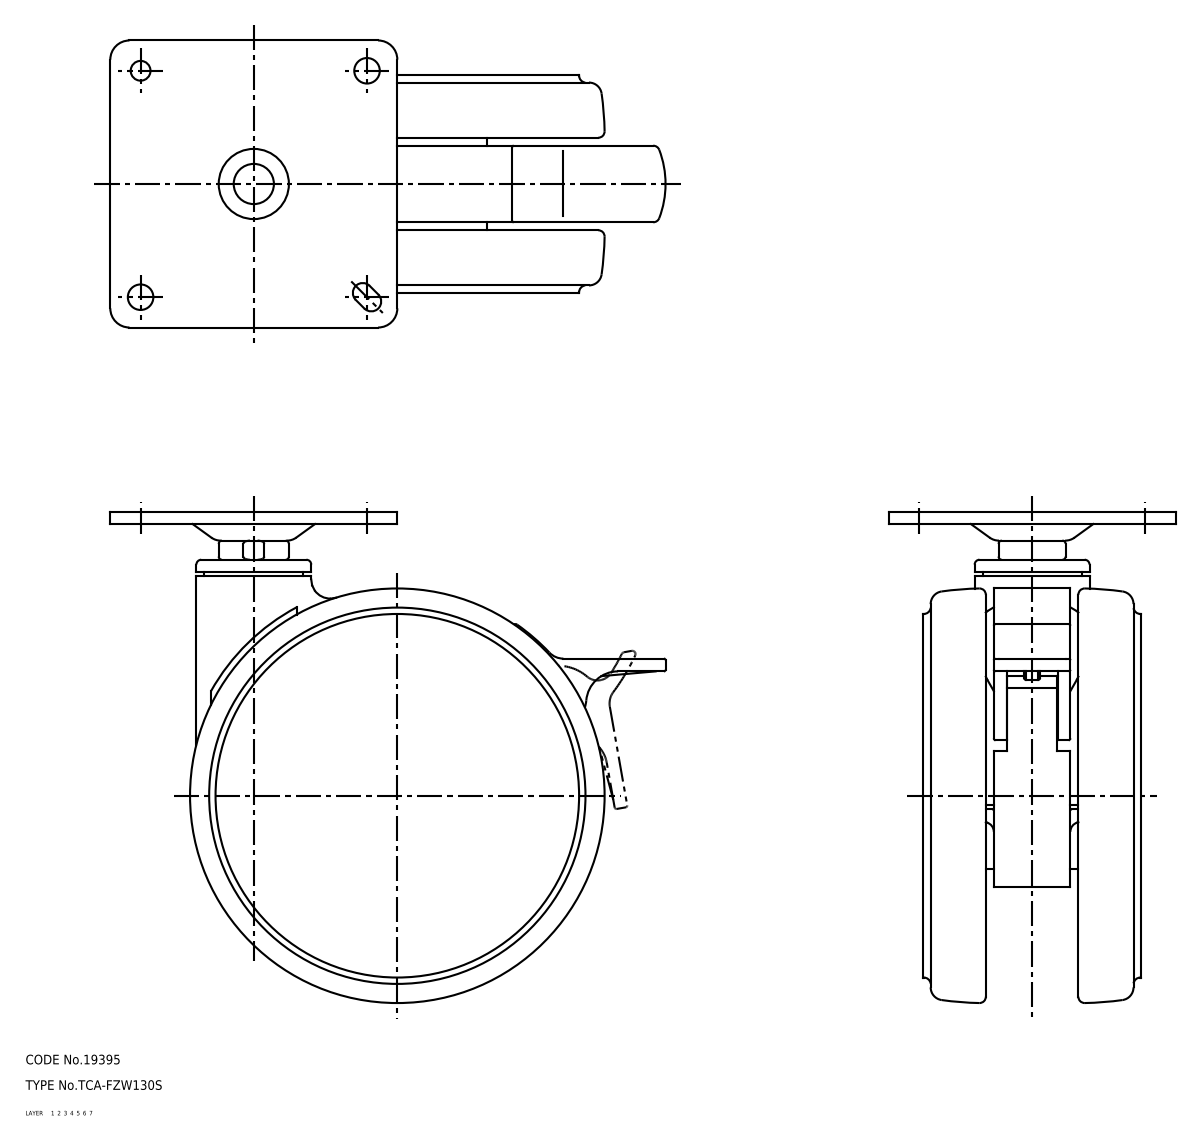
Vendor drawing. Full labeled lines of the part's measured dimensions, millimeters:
Part name (STEP PRODUCT): caster; TCA-FZW130S
STEP written by: SolidWorks 2015 (AUTOMOTIVE_DESIGN)
Units: millimetres
Bodies: 1 solid, 2612 faces (776 planar, 1126 cylindrical, 710 other)
Overall size (bounding box): 174.11 × 154 × 90
Volume: 541 887 mm³ · Surface area: 209 290 mm²
Round holes (diameter × count): ⌀3 ×2, ⌀3.25 ×2, ⌀8 ×2, ⌀1.8 ×1, ⌀3.2 ×1, ⌀6.2 ×1, ⌀9.1 ×1, ⌀10 ×1, ⌀10.1 ×1, ⌀10.5 ×1, ⌀11.5 ×1, ⌀12 ×1
Round bosses / shafts (diameter × count): ⌀117.8 ×1, ⌀114 ×1, ⌀42 ×1, ⌀36 ×1, ⌀31 ×1, ⌀27.9 ×1, ⌀27.6 ×1, ⌀22 ×1
Partial cylindrical surfaces — rounded edges, fillets, slot ends (radius × count): R0.5 ×126, R1.5 ×110, R1 ×74, R0.3 ×44, R2 ×19, R0.2 ×16, R3 ×9, R4 ×5
Main face-to-face distances: 3.8, 2, 66.2, 1.8, 62.4, 64.4, 11.3, 7.5, 56.9, 9.3
Hole centre spacings: 50.2, 71, 31.24, 39.66, 57.03, 100.41
